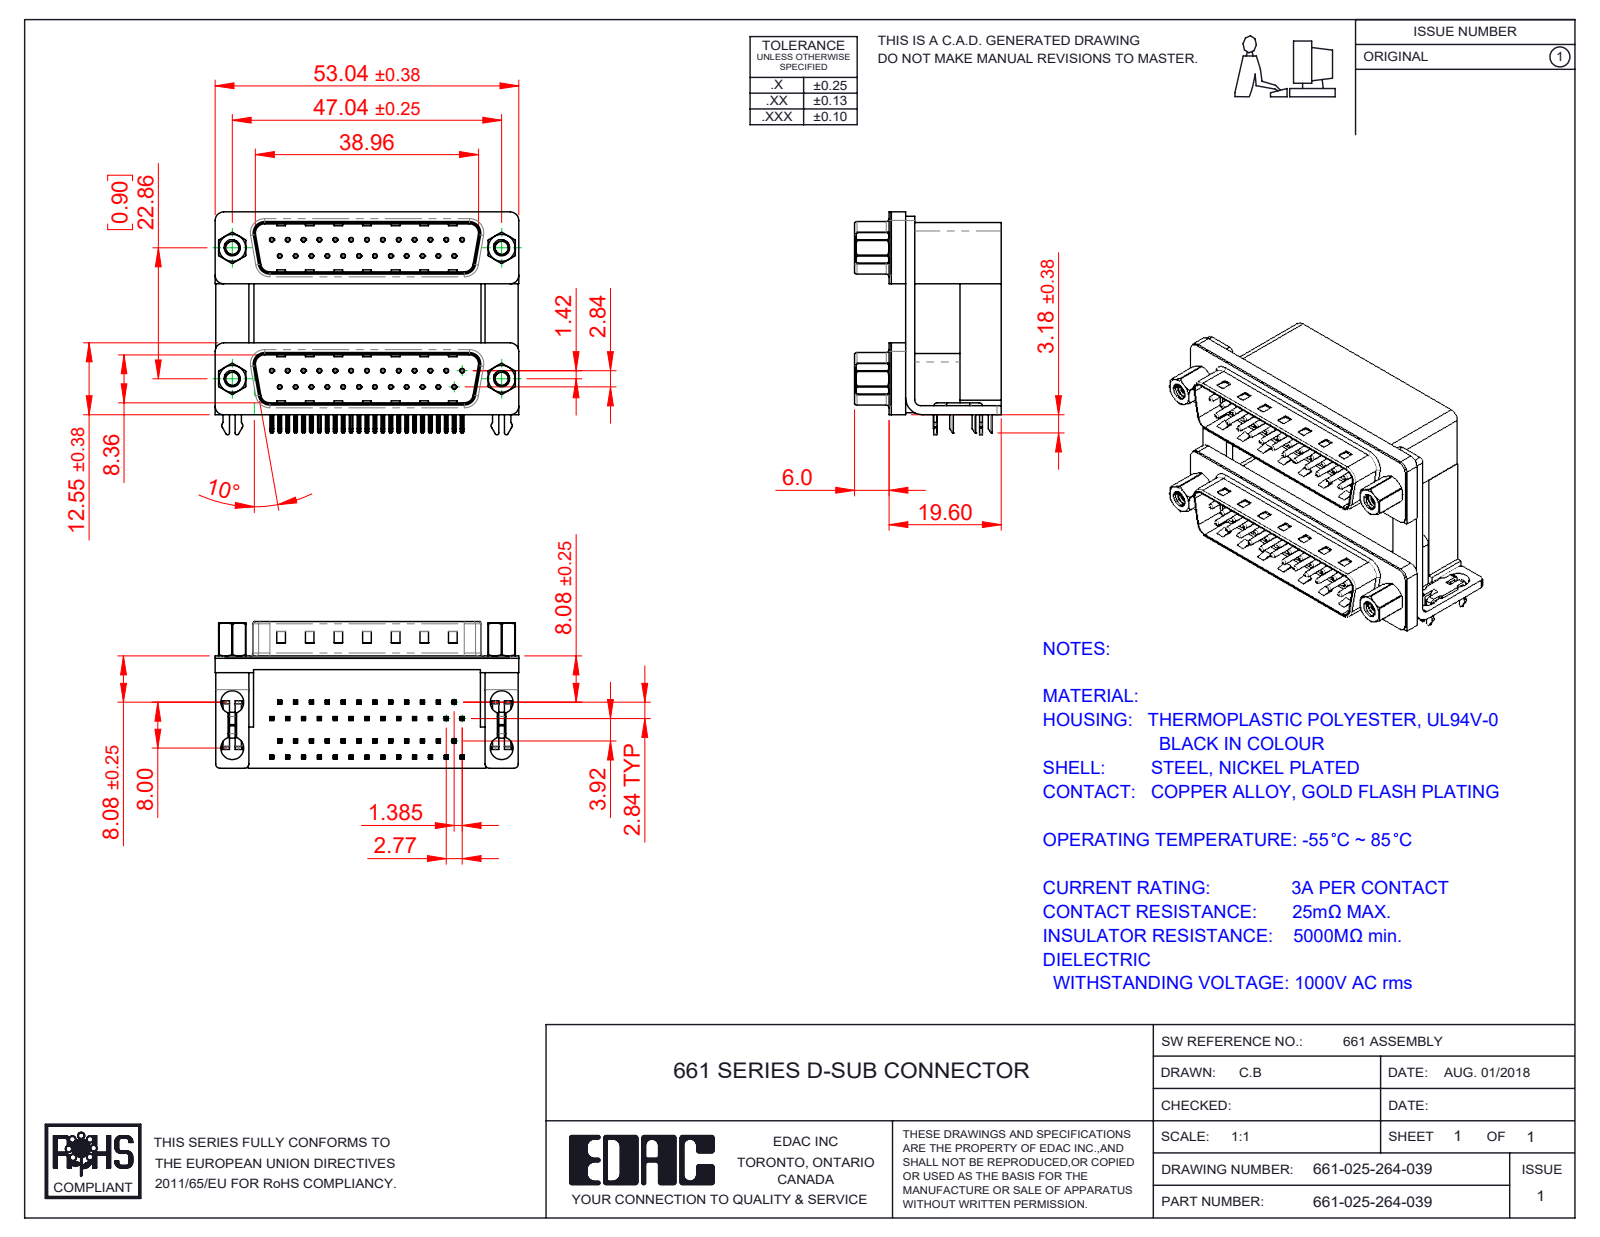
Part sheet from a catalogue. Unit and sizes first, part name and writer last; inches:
Units: inches
Overall size (bounding box): 2.088 × 1.532 × 1.008
Round holes (diameter × count): ⌀0.014 ×50, ⌀0.031 ×50, ⌀0.157 ×8, ⌀0.089 ×4, ⌀0.09 ×4, ⌀0.138 ×4, ⌀0.189 ×4, ⌀0.197 ×4
Round bosses / shafts (diameter × count): ⌀0.03 ×50, ⌀0.193 ×4, ⌀0.187 ×4, ⌀0.154 ×4, ⌀0.11 ×4
Partial cylindrical surfaces — rounded edges, fillets, slot ends (radius × count): R0.01 ×210, R0.005 ×100, R0.02 ×20, R0.059 ×14, R0.03 ×10, R0.035 ×8, R0.063 ×8, R0.079 ×8
Main face-to-face distances: 0.472, 0.016, 0.9, 0.756, 0.283, 0.421, 0.488, 0.657, 0.374, 0.098
Hole centre spacings: 0.109, 0.124, 0.218, 0.327, 0.436, 0.545, 0.654, 0.198
Volume: 1.391 in³ · Surface area: 37.75 in²
Bodies: 67 solids, 5018 faces (3084 planar, 1476 cylindrical, 458 other)
Part name (STEP PRODUCT): 661-025-264-039; 661 Contact Bottom Lower; 661 Housing Lower_25 Contacts; 661 Shell_25 Contacts (+8 more)
STEP written by: SolidWorks 2020 (CONFIG_CONTROL_DESIGN)
